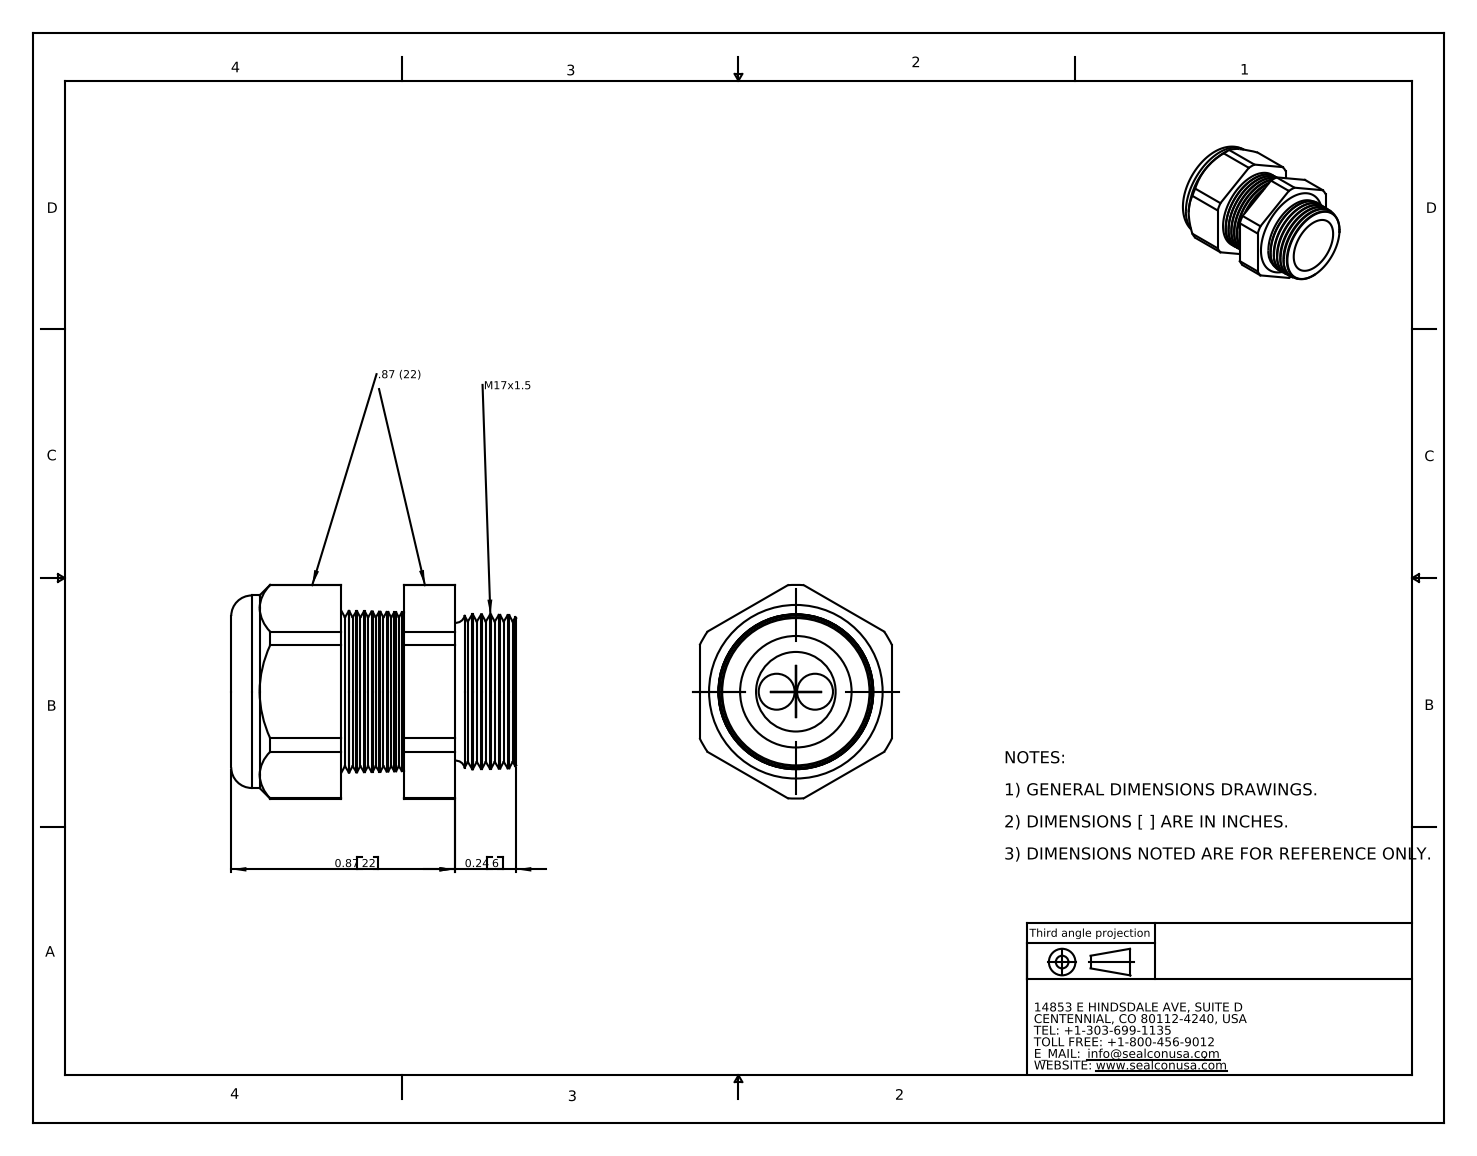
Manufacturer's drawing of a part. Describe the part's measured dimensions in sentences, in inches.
The part is named "CD17M3-BR". Its 3-D file was written by "SolidWorks 2007 (CONFIG_CONTROL_DESIGN)". It is 2 solids with 142 faces: 20 planar, 24 cylindrical and 98 other. Overall it measures 1.11 by 0.833 by 0.75 inches. Its volume is 0.322 cubic inches and its surface area 5.863 square inches. Round holes: 2 of diameter 0.14, 1 of diameter 0.29, 1 of diameter 0.31. Round bosses or shafts: 1 of diameter 0.75. Partial cylindrical surfaces (rounded edges, fillets, slot ends): 1 of radius 0.416. The main face-to-face distances are 0.75, 0.673, 0.429, 0.244, 0.87, 0.441, 0.197, 1.11, 0.681, 0.437. The hole center spacings are 0.075, 0.15.
